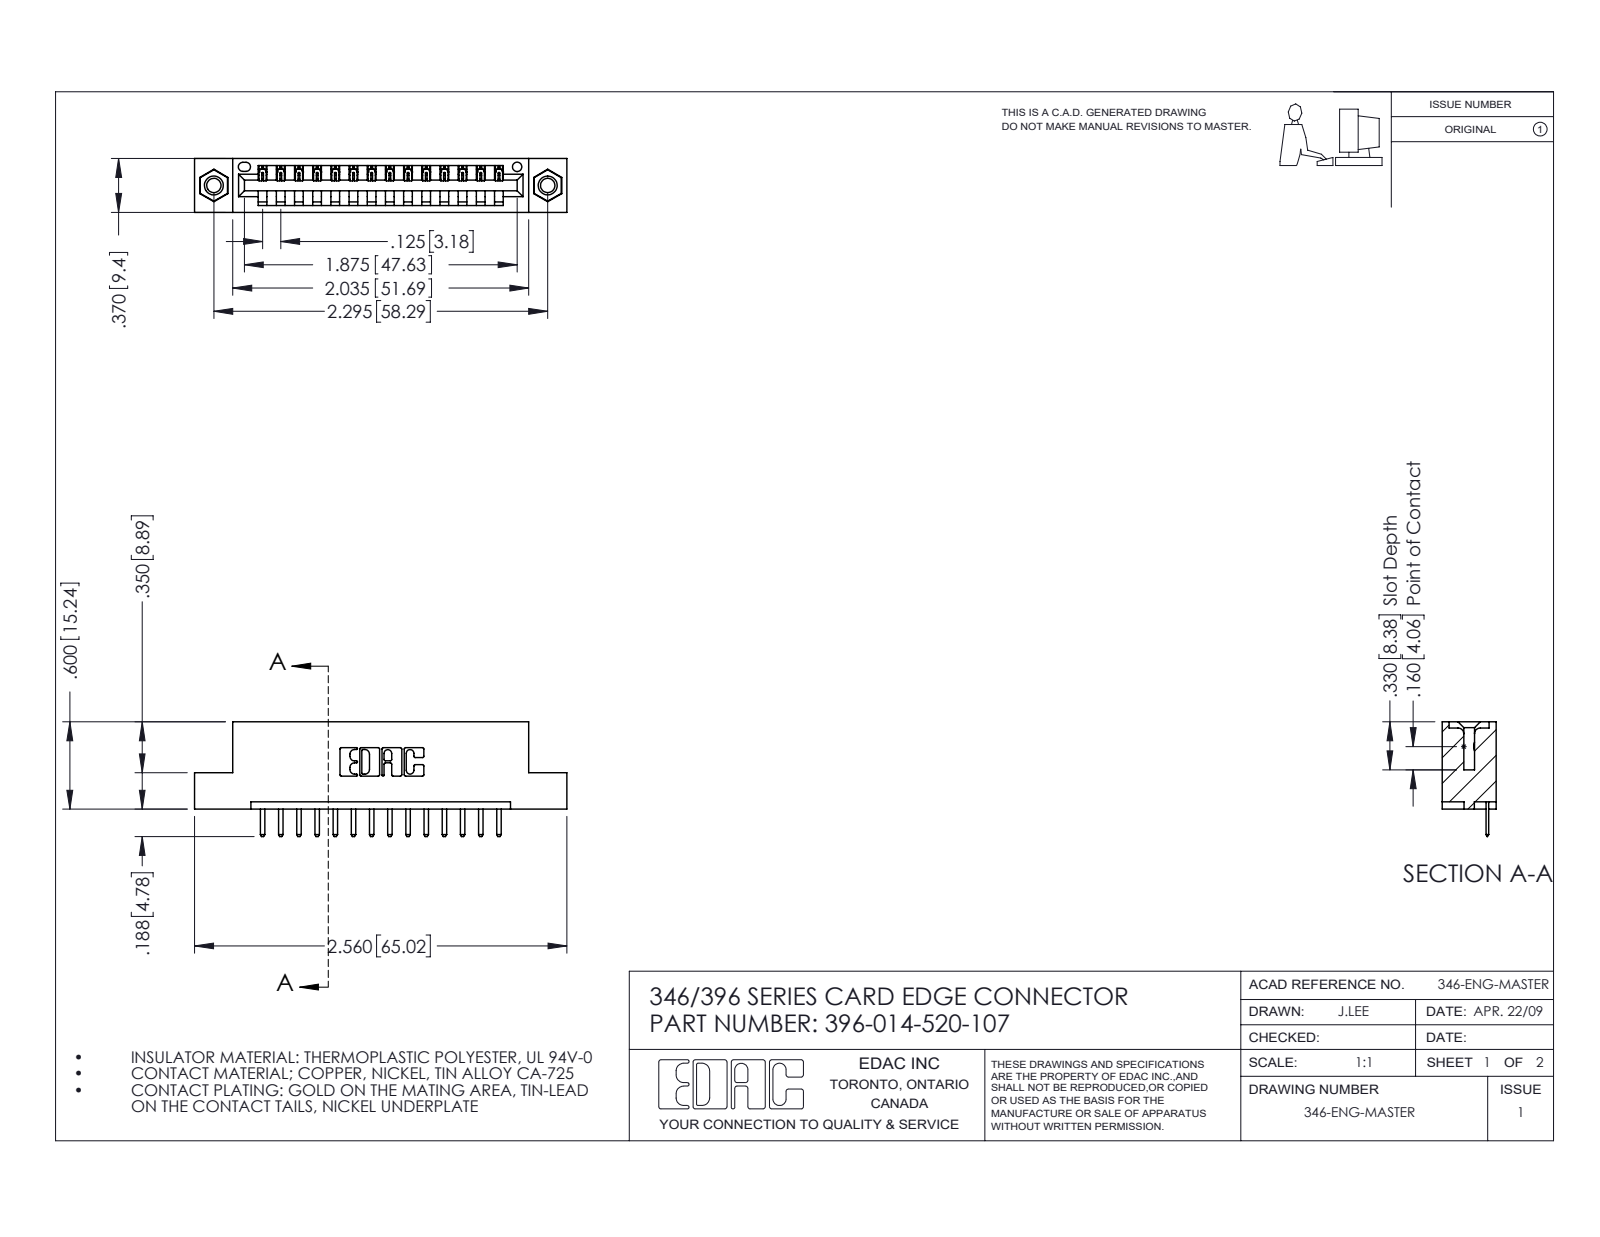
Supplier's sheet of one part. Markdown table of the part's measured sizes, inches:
| quantity | value |
| --- | --- |
| part name | 346 Part_Flush Mounting Lugs - 0.156 Dia-TI; 345-292-001_345-293-120; 345-250-001_345-250-005-103; 396-014-520-107 |
| STEP written by | SolidWorks 2016 (CONFIG_CONTROL_DESIGN) |
| units | inches |
| bodies | 17 solids, 1050 faces (696 planar, 338 cylindrical, 16 other) |
| overall size | 2.56 × 0.788 × 0.37 |
| volume | 0.365 in³ |
| surface area | 10.96 in² |
| round holes (diameter × count) | 0.098 × 2, 0.125 × 2, 0.156 × 2, 0.064 × 1 |
| round bosses / shafts (diameter × count) | 0.155 × 2 |
| partial cylindrical surfaces (radius × count) | 0.01 × 30, 0.006 × 28, 0.01 × 22, 0.007 × 6, 0.031 × 6, 0.026 × 3, 0.031 × 2, 0.04 × 2 |
| main face-to-face distances | 0.25, 0.37, 0.048, 0.322, 0.148, 0.222, 0.1, 0.174, 0.072, 0.298 |
| hole center spacings | 0.246, 2.089, 2.295 |
